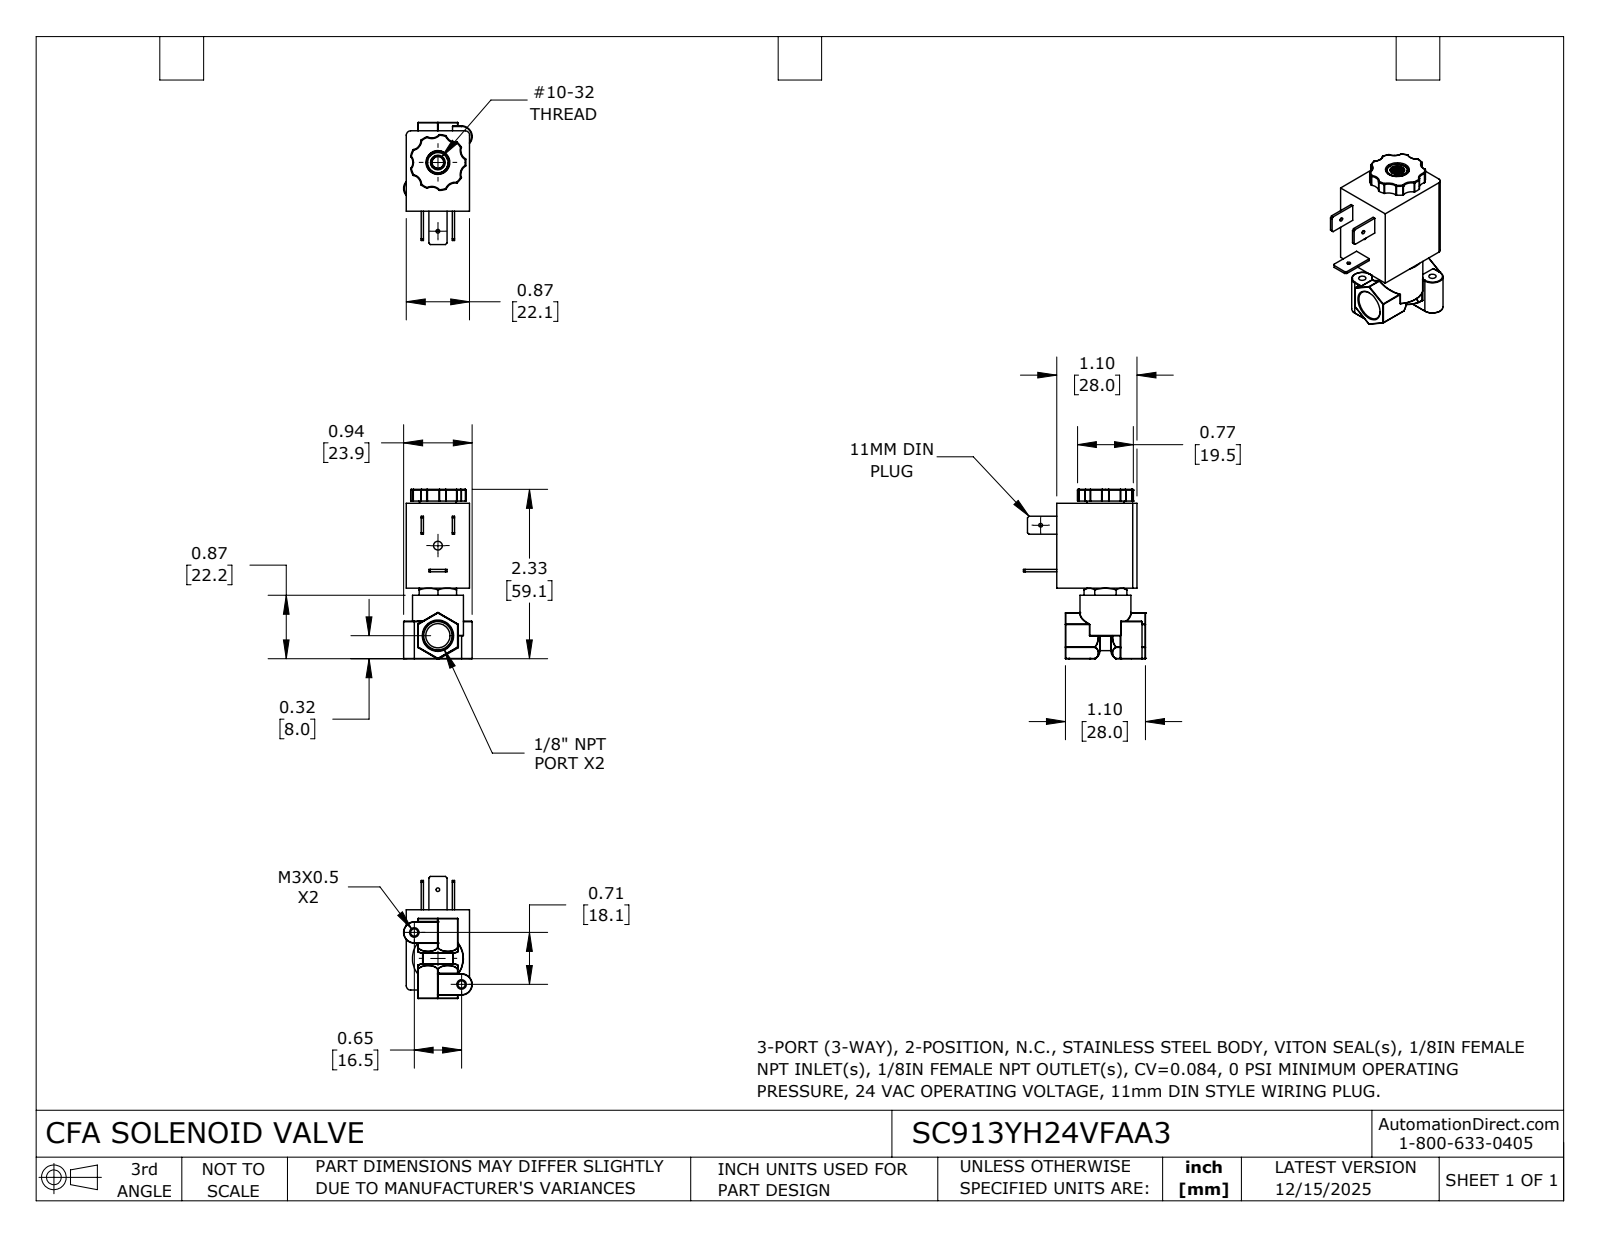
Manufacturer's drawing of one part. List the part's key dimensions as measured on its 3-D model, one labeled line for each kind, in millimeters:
Part name (STEP PRODUCT): SC913YH24VFAA3
STEP written by: SolidWorks 2024 (CONFIG_CONTROL_DESIGN)
Units: millimetres
Bodies: 1 solid, 363 faces (70 planar, 142 cylindrical, 151 other)
Overall size (bounding box): 59.1 × 42.6 × 23.9
Volume: 25 780 mm³ · Surface area: 8 955 mm²
Round holes (diameter × count): ⌀1.3 ×2, ⌀2.5 ×2, ⌀3 ×1, ⌀4.1 ×1, ⌀8.3 ×1, ⌀8.4 ×1
Round bosses / shafts (diameter × count): ⌀17.8 ×1, ⌀8 ×1
Partial cylindrical surfaces — rounded edges, fillets, slot ends (radius × count): R0.1 ×29, R0.3 ×18, R0.2 ×12, R3.4 ×7, R0.4 ×2, R1.5 ×2, R3.4 ×2, R3.7 ×2
Main face-to-face distances: 22.1, 28, 29.6, 13.9, 34.5, 4.8, 4.1, 18, 24.7, 54.3
Hole centre spacings: 12.3, 17.1, 24, 24.5, 31.4, 34.1
